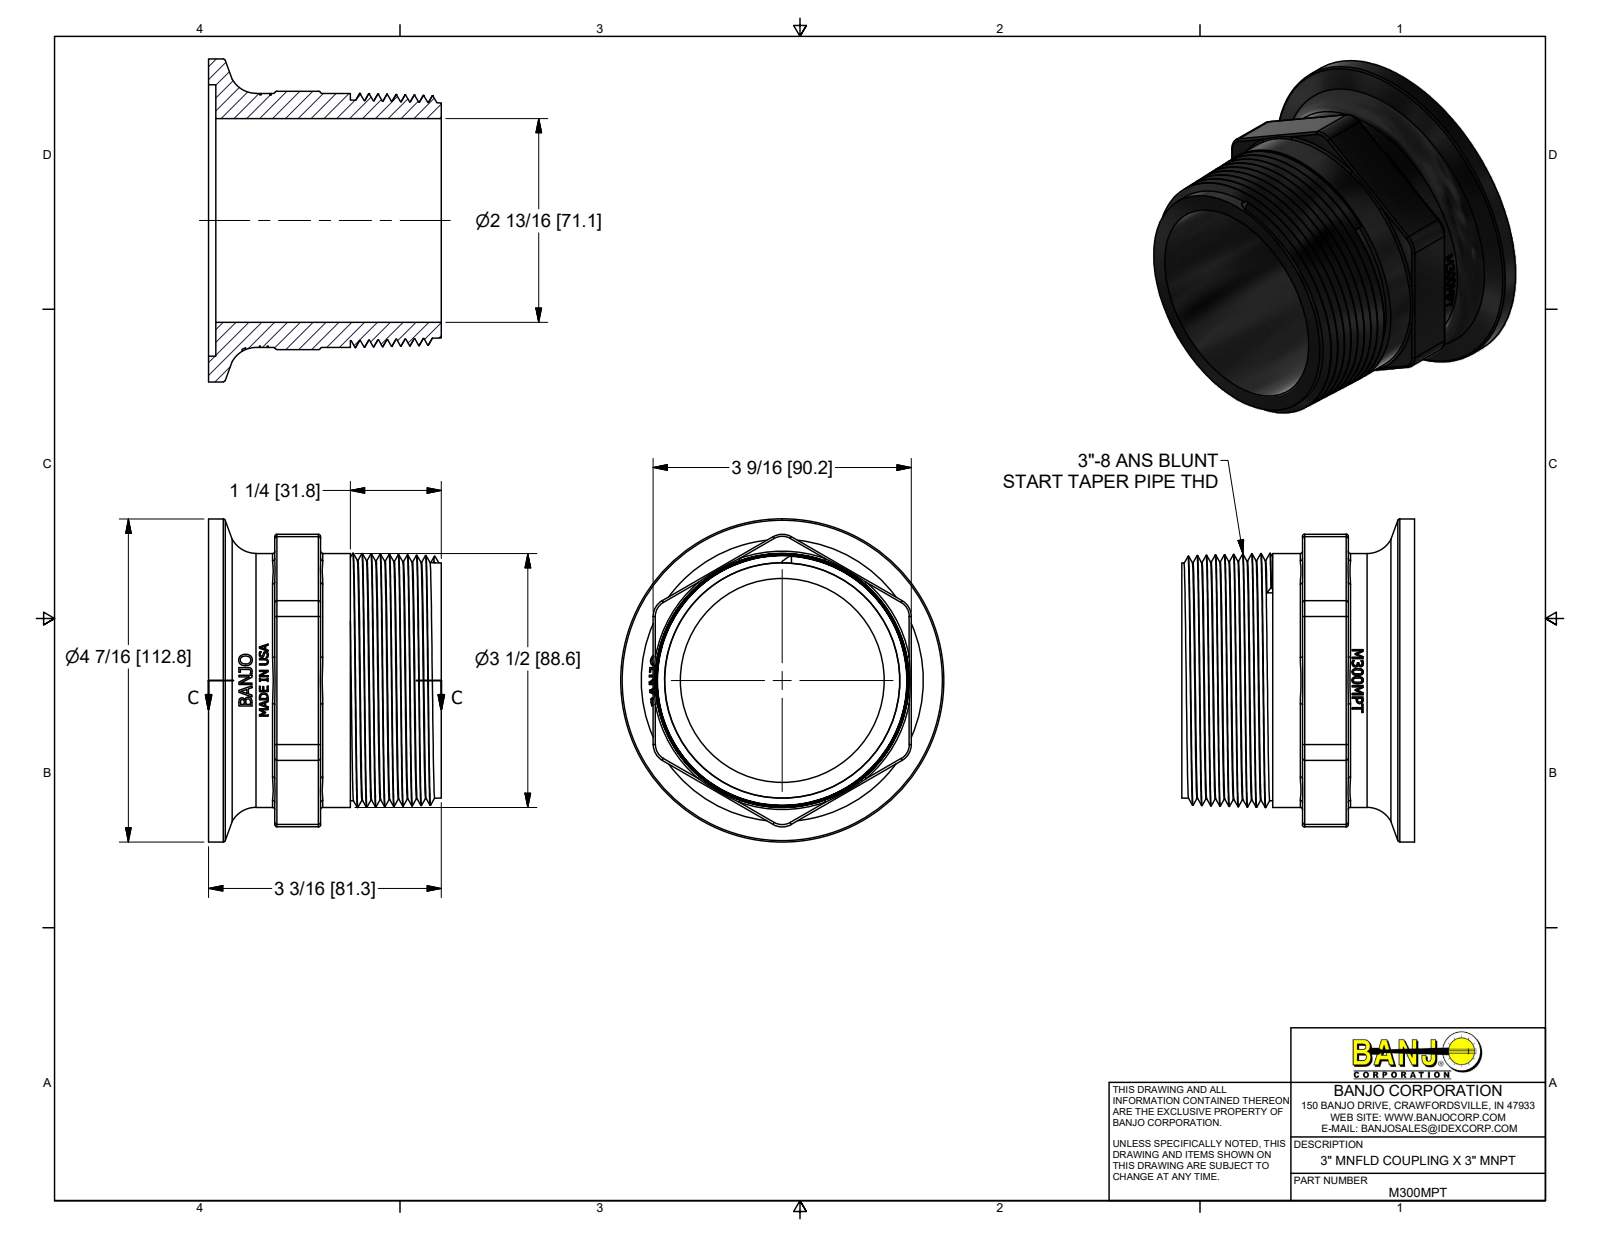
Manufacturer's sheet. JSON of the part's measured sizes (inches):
{"part_name": "M300MPT", "step_written_by": "Autodesk Inventor 2018 (AUTOMOTIVE_DESIGN)", "units": "inches", "bodies": {"solids": 1, "faces": 421, "planar": 189, "cylindrical": 45, "other": 187}, "overall_size": [4.44, 4.44, 3.2], "volume_in3": 12.28, "surface_area_in2": 93.26, "round_holes": [[2.8, 1], [3.73, 1]], "round_bosses_or_shafts": [[4.44, 1], [3.49, 1]], "partial_cylinders_radius": [[0.03, 12], [0.25, 6], [1.725, 1]], "face_to_face_distances": [0.1, 3.55, 3.2, 3.1, 1.95, 1.85, 1.25, 0.91, 0.81, 1.04]}
